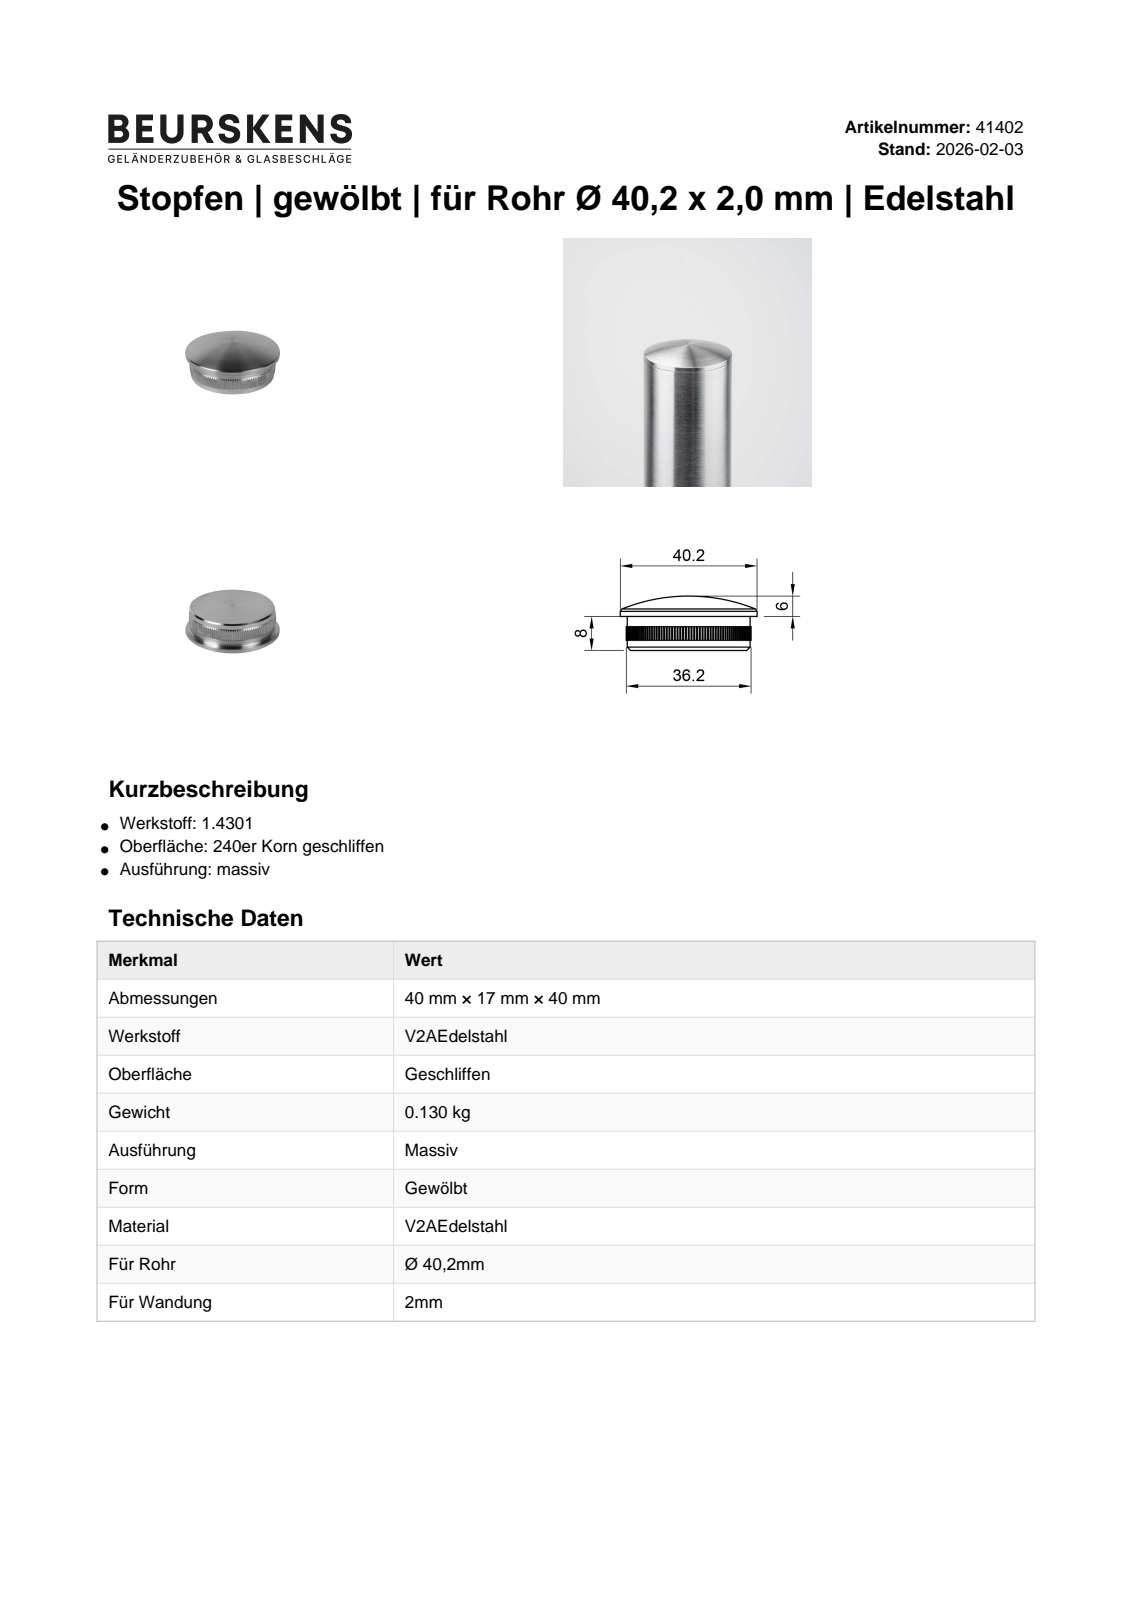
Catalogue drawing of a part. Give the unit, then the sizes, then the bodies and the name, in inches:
Units: inches
Overall size (bounding box): 1.583 × 1.583 × 0.63
Round bosses / shafts (diameter × count): ⌀1.583 ×1, ⌀1.421 ×1
Partial cylindrical surfaces — rounded edges, fillets, slot ends (radius × count): R0.005 ×140, R0.722 ×1
Main face-to-face distances: 0.394, 0.118, 0.276, 0.157
Volume: 0.94 in³ · Surface area: 6.254 in²
Bodies: 1 solid, 290 faces (4 planar, 283 cylindrical, 3 other)
Part name (STEP PRODUCT): 41402
STEP written by: Autodesk Inventor 2022 (AUTOMOTIVE_DESIGN)
